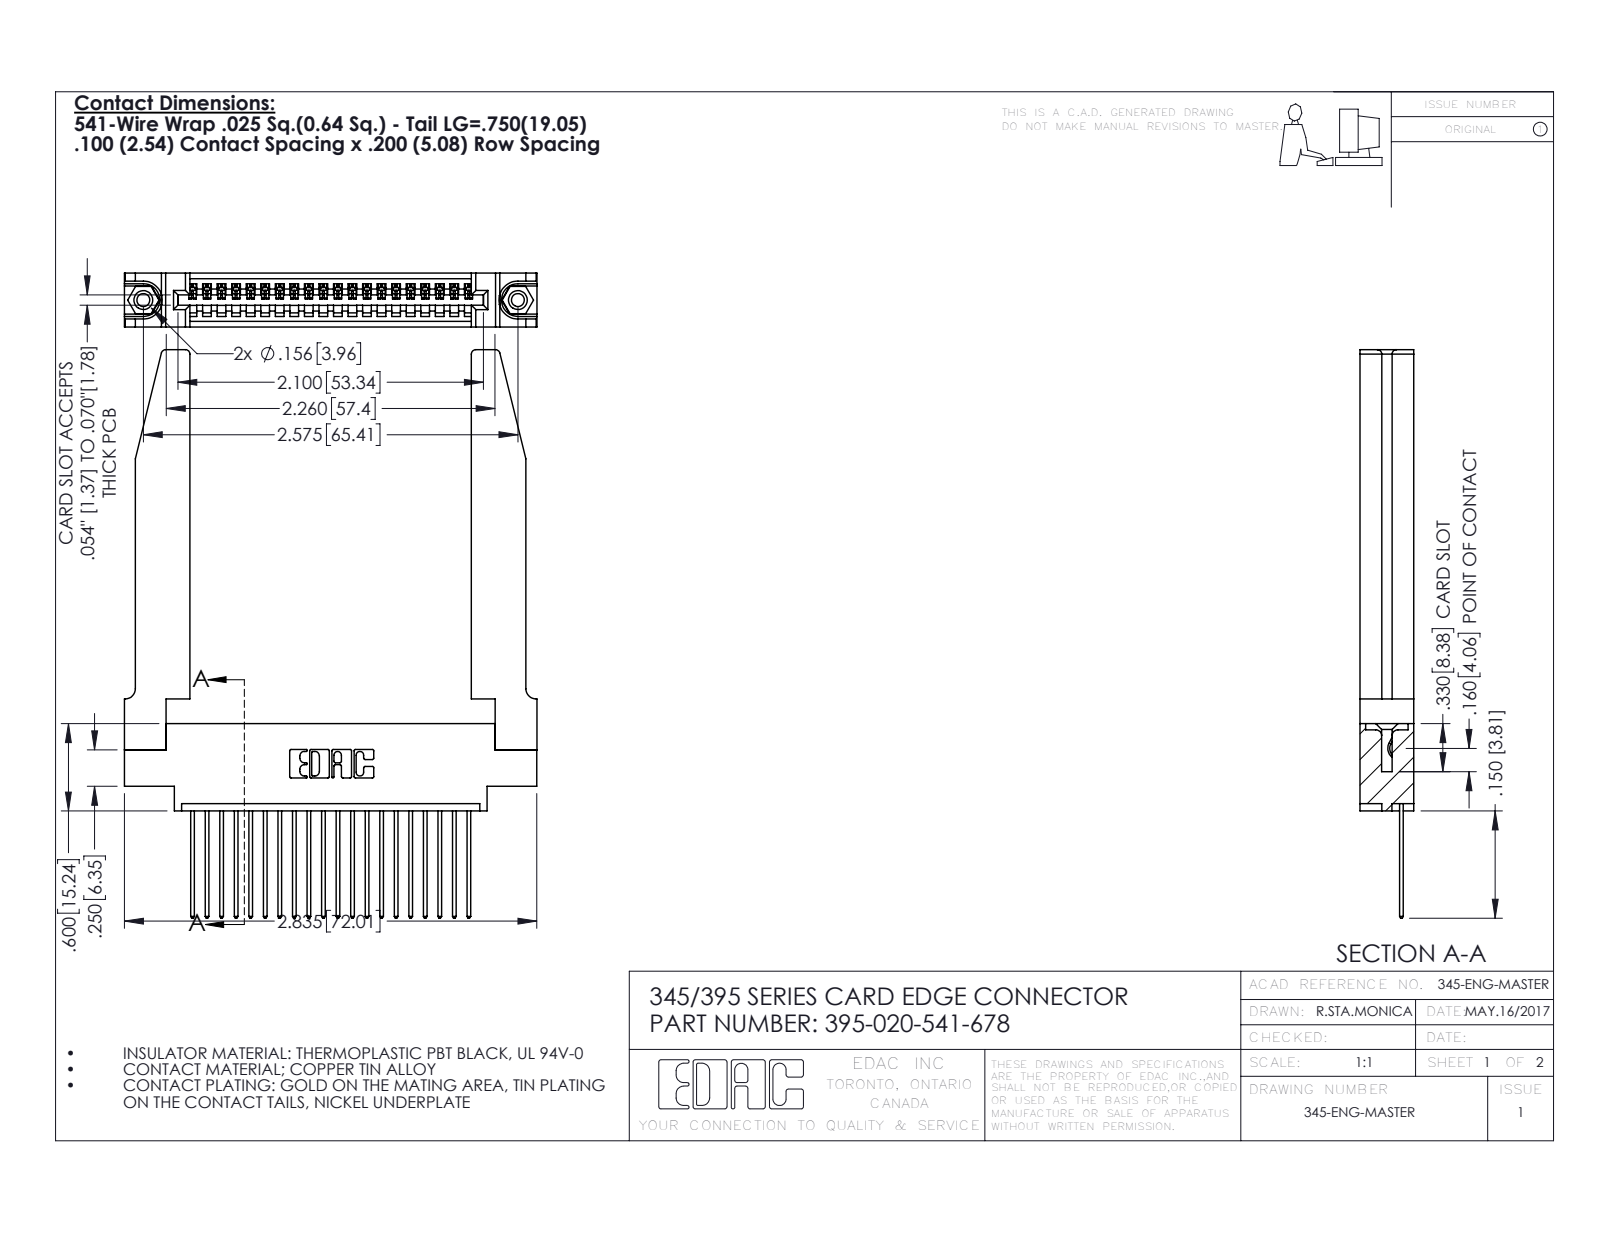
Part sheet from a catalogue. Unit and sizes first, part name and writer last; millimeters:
Units: millimetres
Overall size (bounding box): 99.2 × 72 × 9.4
Round holes (diameter × count): ⌀2.3 ×2, ⌀3.2 ×2, ⌀4 ×2, ⌀1.6 ×1
Round bosses / shafts (diameter × count): ⌀3.9 ×2
Partial cylindrical surfaces — rounded edges, fillets, slot ends (radius × count): R0.2 ×40, R0.3 ×40, R0.3 ×22, R0.8 ×8, R0.2 ×6, R0.8 ×6, R0.7 ×3, R0.8 ×2
Main face-to-face distances: 9.4, 1.8, 7.6, 2.5, 6.9, 0.6, 5.1, 3.8, 3.8, 5.6
Hole centre spacings: 6.9, 59.5, 65.4
Volume: 14 400 mm³ · Surface area: 15 850 mm²
Bodies: 25 solids, 1524 faces (1026 planar, 446 cylindrical, 52 other)
Part name (STEP PRODUCT): 345-250-001_345-250-001-102; 345-220-078_345-220-078; 345-292-001_345-293-141; 395-020-541-678 (+1 more)
STEP written by: SolidWorks 2016 (CONFIG_CONTROL_DESIGN)
